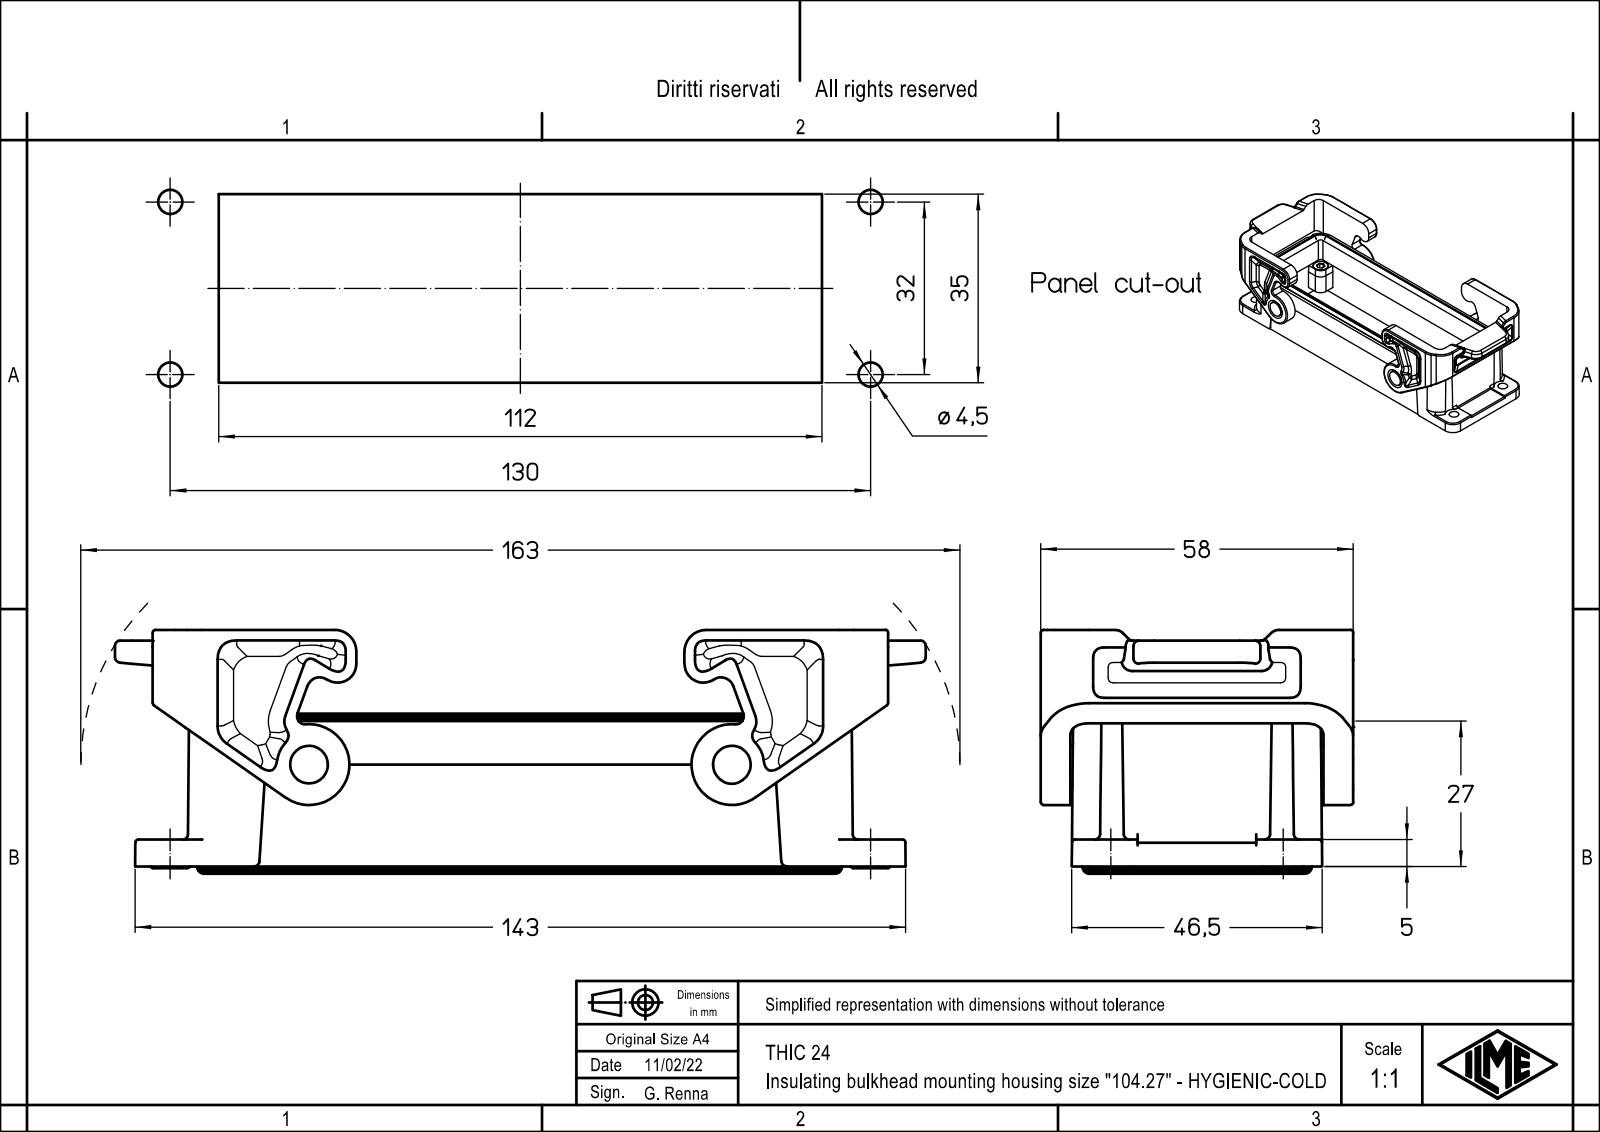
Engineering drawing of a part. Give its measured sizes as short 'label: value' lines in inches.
name: 53623; THIH_24
written by: Creo Elements/Direct Modeling 20.1B 02-Apr-2019 (C) Parametric Technology GmbH (AUTOMOTIVE_DESIGN)
unit: in
bodies: 1 solid, 714 faces (310 planar, 220 cylindrical, 184 other)
size: 5.925 × 2.283 × 1.781
volume: 4.778 in³; area: 64.63 in²
holes: 4× ⌀0.098, 4× ⌀0.177, 2× ⌀0.283
bosses: 4× ⌀0.189, 2× ⌀0.276
rounds: 28× R0.039, 16× R0.051, 14× R0.059, 12× R0.079, 12× R0.118, 12× R0.217, 10× R0.106, 8× R0.197
face distances: 0.232, 1.618, 1.386, 0.217, 2.067, 0.449, 1.835, 1.85, 0.281, 4.699
hole spacings: 0.521, 1.269, 4.607, 4.75, 1.063, 1.26, 4.094, 4.23
